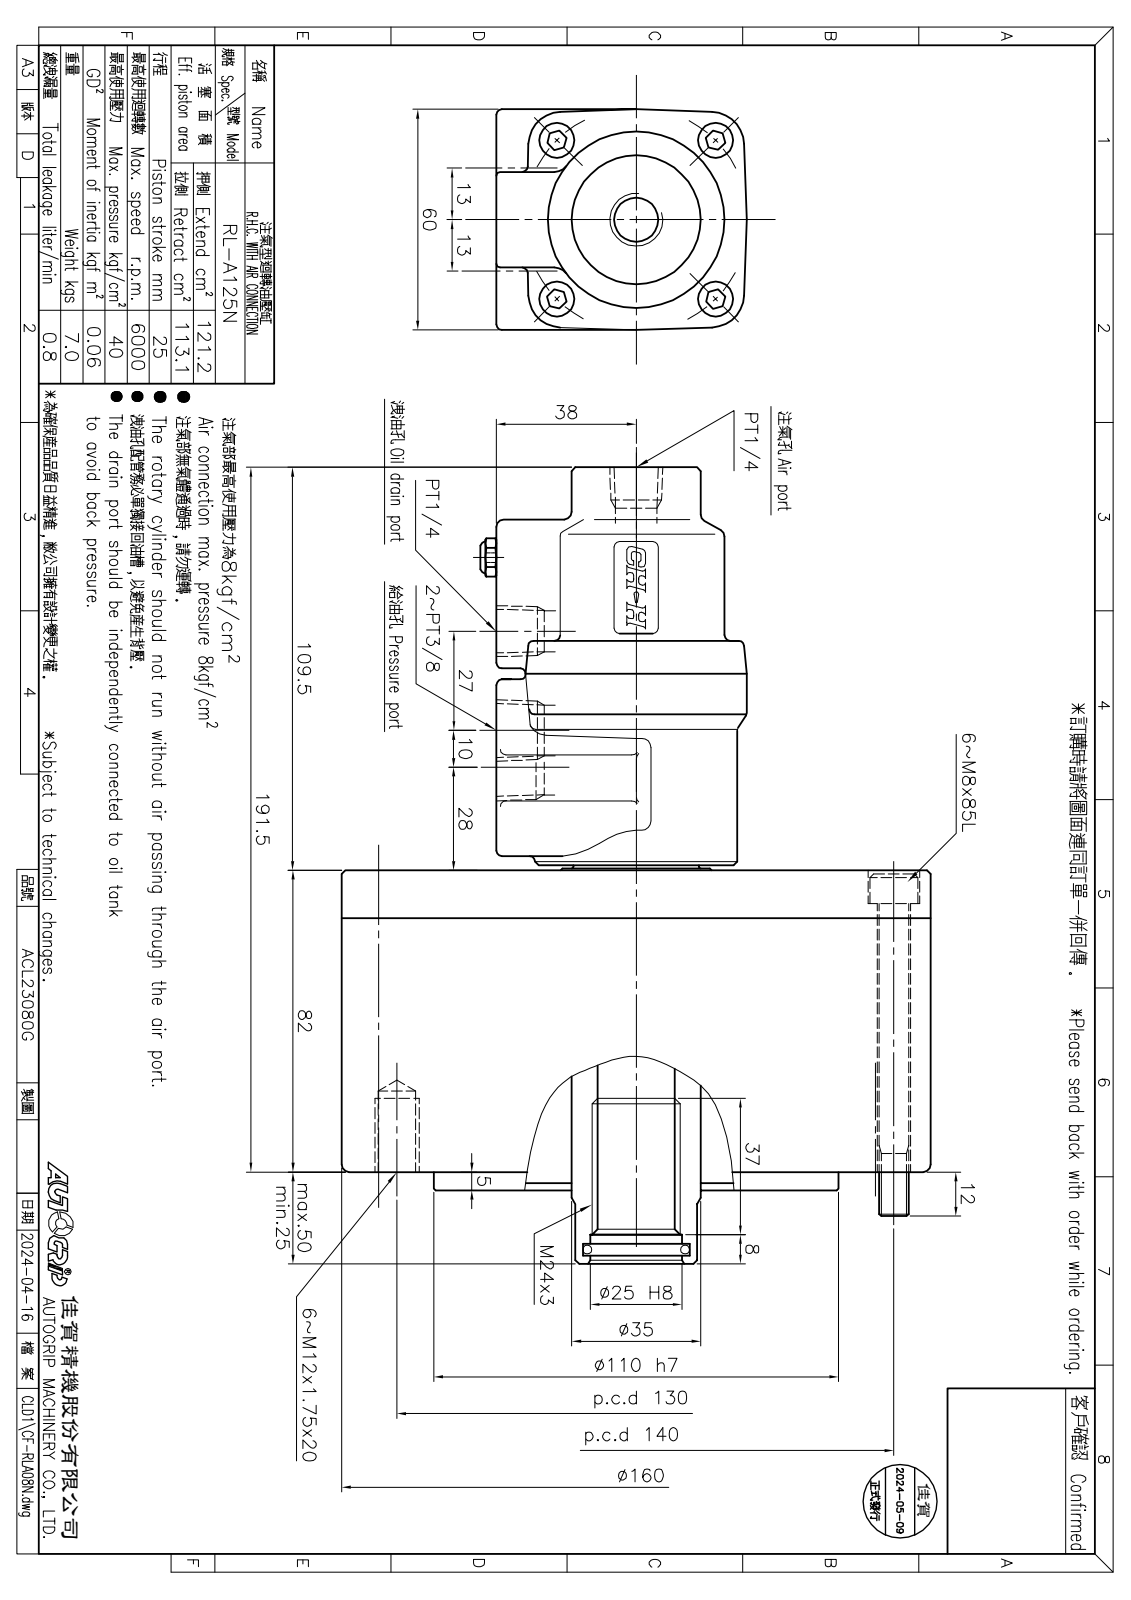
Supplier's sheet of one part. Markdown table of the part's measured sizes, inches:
| quantity | value |
| --- | --- |
| part name | RL-125活塞; RK-125缸體; RL-A100N消音器; RL-A125N組合件 |
| STEP written by | SolidWorks 2010 (CONFIG_CONTROL_DESIGN) |
| units | inches |
| bodies | 6 solids, 415 faces (90 planar, 154 cylindrical, 171 other) |
| overall size | 8.524 × 6.299 × 6.299 |
| volume | 99.41 in³ |
| surface area | 385.1 in² |
| round holes (diameter × count) | 0.354 × 6, 0.402 × 6, 0.472 × 6, 0.551 × 6, 0.441 × 2, 0.579 × 2, 0.102 × 1, 0.161 × 1, 0.197 × 1, 0.827 × 1, 0.945 × 1, 0.984 × 1 |
| round bosses / shafts (diameter × count) | 6.299 × 1, 4.921 × 1, 4.331 × 1, 2.165 × 1, 1.89 × 1, 1.378 × 1, 1.299 × 1, 0.15 × 1 |
| partial cylindrical surfaces (radius × count) | 0.059 × 24, 0.236 × 4, 0.354 × 4, 0.079 × 3, 0.197 × 2, 0.591 × 2 |
| main face-to-face distances | 0.984, 0.787, 0.512, 0.276, 2.244, 1.732, 1.457, 1.26, 0.748, 0.472 |
| hole center spacings | 2.756, 2.559, 2.042, 3.239, 4.433, 4.773, 4.911, 0.72 |
